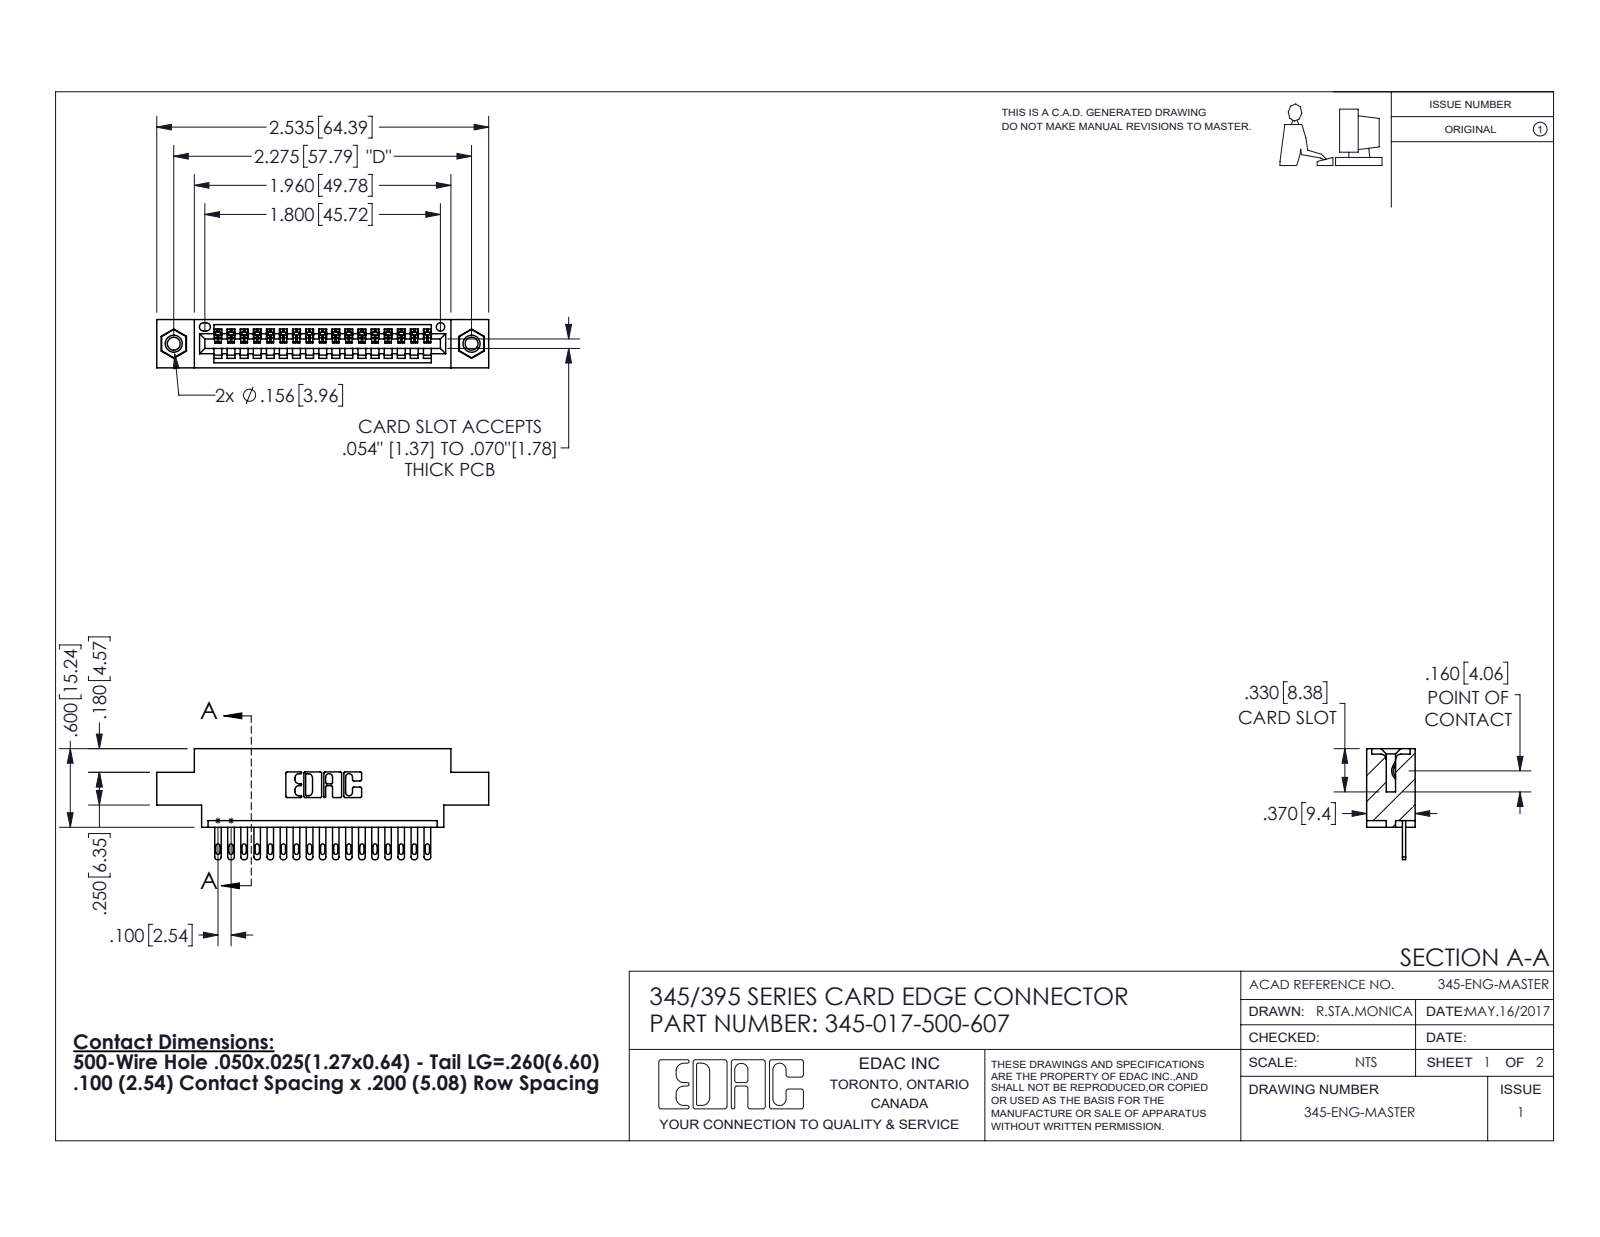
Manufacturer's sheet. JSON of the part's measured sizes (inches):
{"part_name": "345-292-001_345-293-100; 345-250-001_345-250-005-103; 345 Part_0.170 Offset - 0.156 Dia-TI; 345-017-500-607", "step_written_by": "SolidWorks 2016 (CONFIG_CONTROL_DESIGN)", "units": "inches", "bodies": {"solids": 20, "faces": 1108, "planar": 694, "cylindrical": 398, "other": 16}, "overall_size": [2.535, 0.847, 0.37], "volume_in3": 0.354, "surface_area_in2": 11.71, "round_holes": [[0.098, 2], [0.125, 2], [0.156, 2], [0.064, 1]], "round_bosses_or_shafts": [[0.155, 2]], "partial_cylinders_radius": [[0.006, 34], [0.016, 34], [0.02, 34], [0.01, 22], [0.007, 6], [0.031, 6], [0.026, 3], [0.031, 2]], "face_to_face_distances": [0.072, 0.298, 0.37, 0.2, 0.098, 0.272, 0.025, 0.225, 0.1, 0.15], "hole_center_spacings": [0.27, 2.041, 2.275]}
